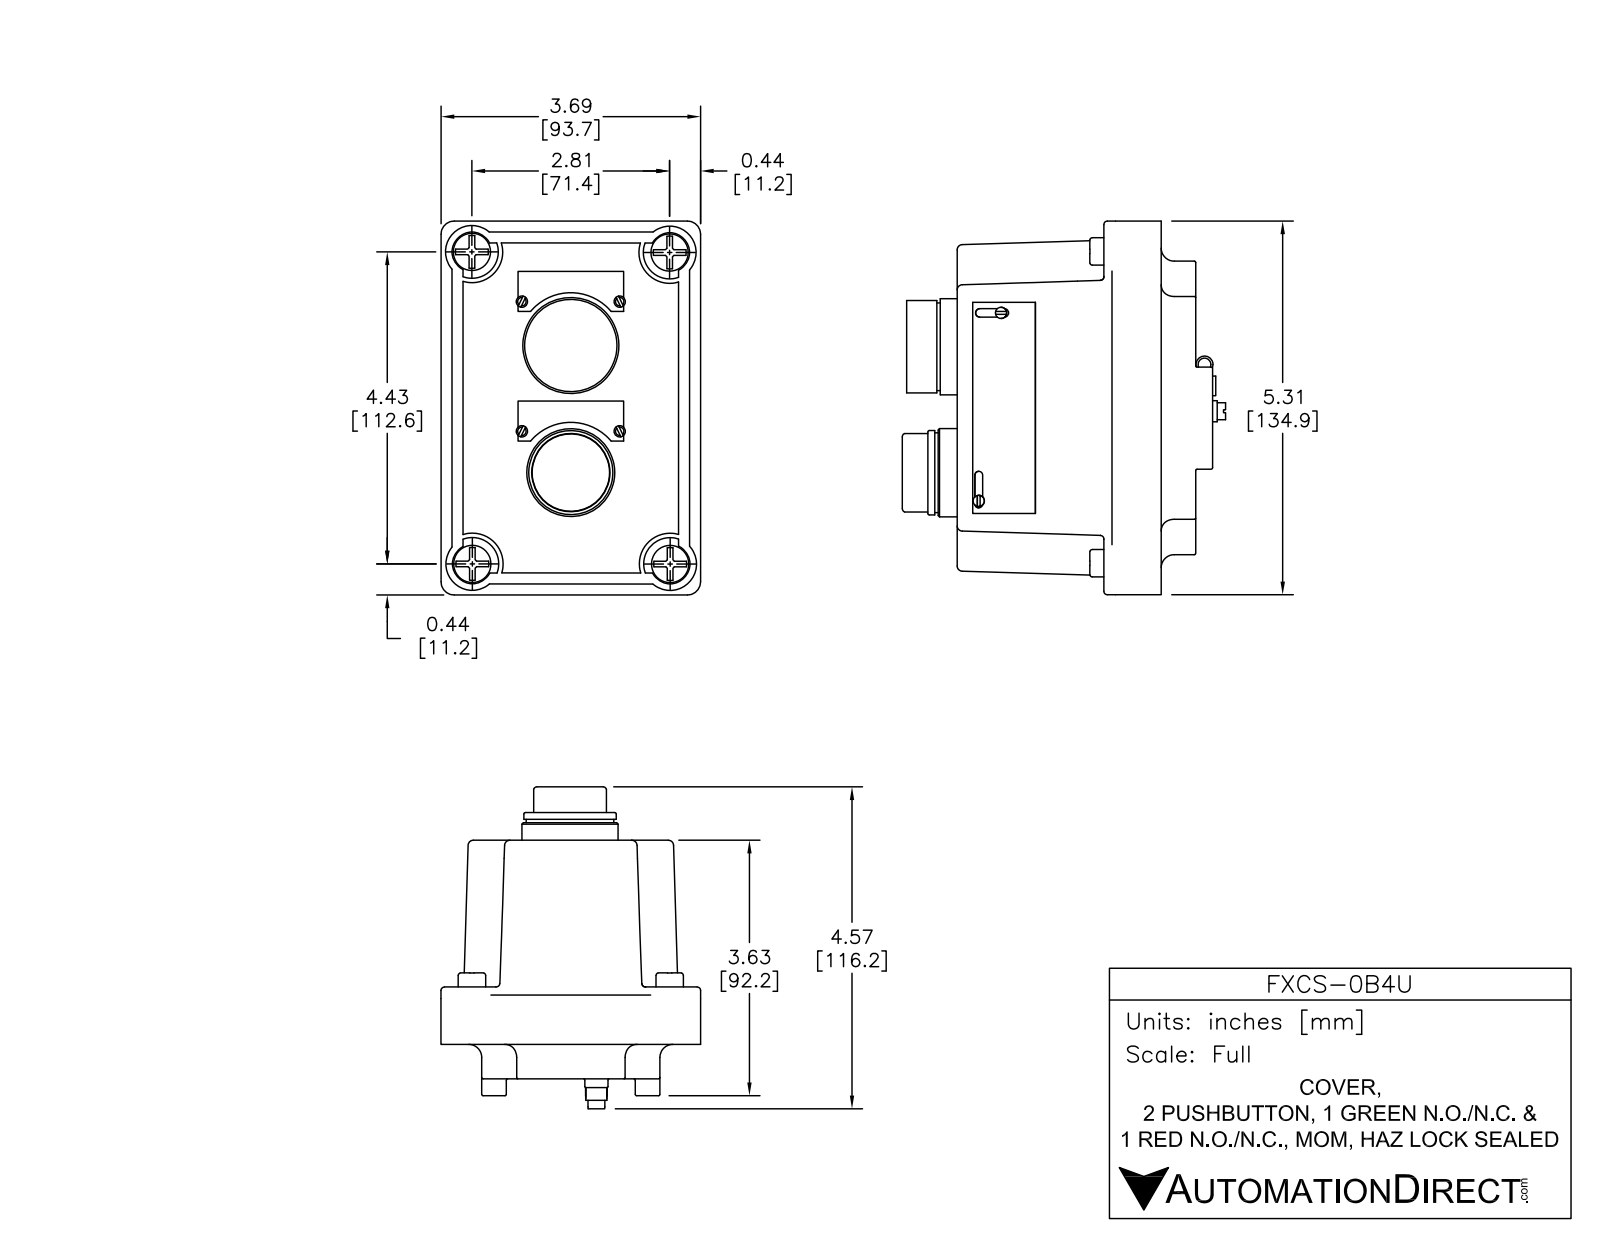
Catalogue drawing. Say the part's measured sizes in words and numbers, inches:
The part is named "FXCS-0B4U". Its 3-D file was written by "SolidWorks 2015 (AUTOMOTIVE_DESIGN)". It is 2 solids with 729 faces: 299 planar, 163 cylindrical and 267 other. Overall it measures 5.31 by 4.565 by 3.69 inches. Its volume is 49.58 cubic inches and its surface area 105.7 square inches. Round holes: 8 of diameter 0.16, 2 of diameter 1.152, 1 of diameter 0.198. Round bosses or shafts: 8 of diameter 0.16, 4 of diameter 0.39, 2 of diameter 1.366, 2 of diameter 1.312, 2 of diameter 1.246, 2 of diameter 1.04, 1 of diameter 0.33, 1 of diameter 0.3. Partial cylindrical surfaces (rounded edges, fillets, slot ends): 22 of radius 0.02, 12 of radius 0.05, 4 of radius 0.055, 4 of radius 0.06, 4 of radius 0.075, 4 of radius 0.185, 4 of radius 0.42, 3 of radius 0.653. The main face-to-face distances are 3.39, 0.49, 2.9, 0.02, 3.69, 0.578, 3.111, 1.19, 0.7, 2.2. The hole center spacings are 0.25, 2.197, 0.5, 2.183, 2.239, 0.75, 1.205, 1.265.
